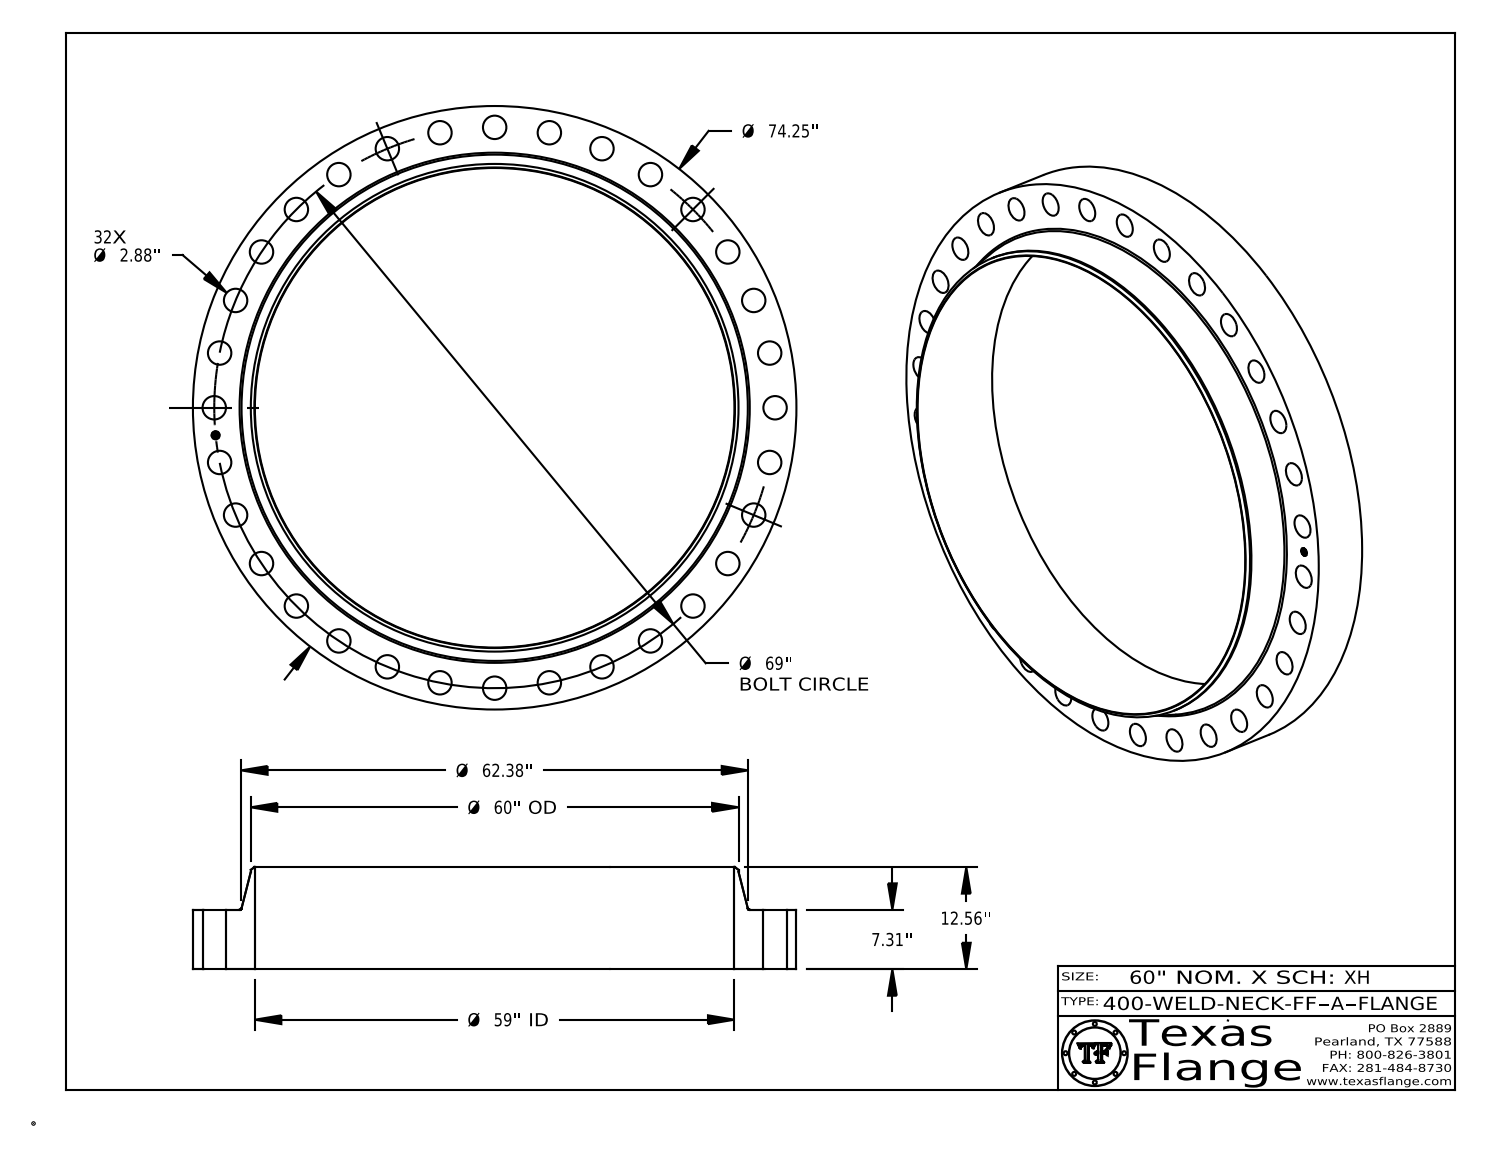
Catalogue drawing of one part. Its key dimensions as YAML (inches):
part_name: "400-WELD-NECK-FF, Series A"
step_written_by: "CATIA V5 STEP AP214 (AUTOMOTIVE_DESIGN)"
units: inches
bodies: {solids: 1, faces: 464, planar: 368, cylindrical: 90, other: 6}
overall_size: [74.25, 74.25, 12.56]
volume: 11153
surface_area: 9678
round_holes:
  - {diameter: 2.88, count: 32}
  - {diameter: 1, count: 1}
  - {diameter: 59, count: 1}
round_bosses_or_shafts:
  - {diameter: 0.061, count: 8}
  - {diameter: 74.25, count: 1}
  - {diameter: 60, count: 1}
  - {diameter: 0.788, count: 1}
face_to_face_distances: [7.31, 12.56, 5.25, 0.015, 7.295, 5.265, 0.298, 0.292, 0.054, 0.193]
hole_center_spacings: [60.853, 66.029, 57.372, 67.674, 48.791, 34.5, 13.461, 32.526]
